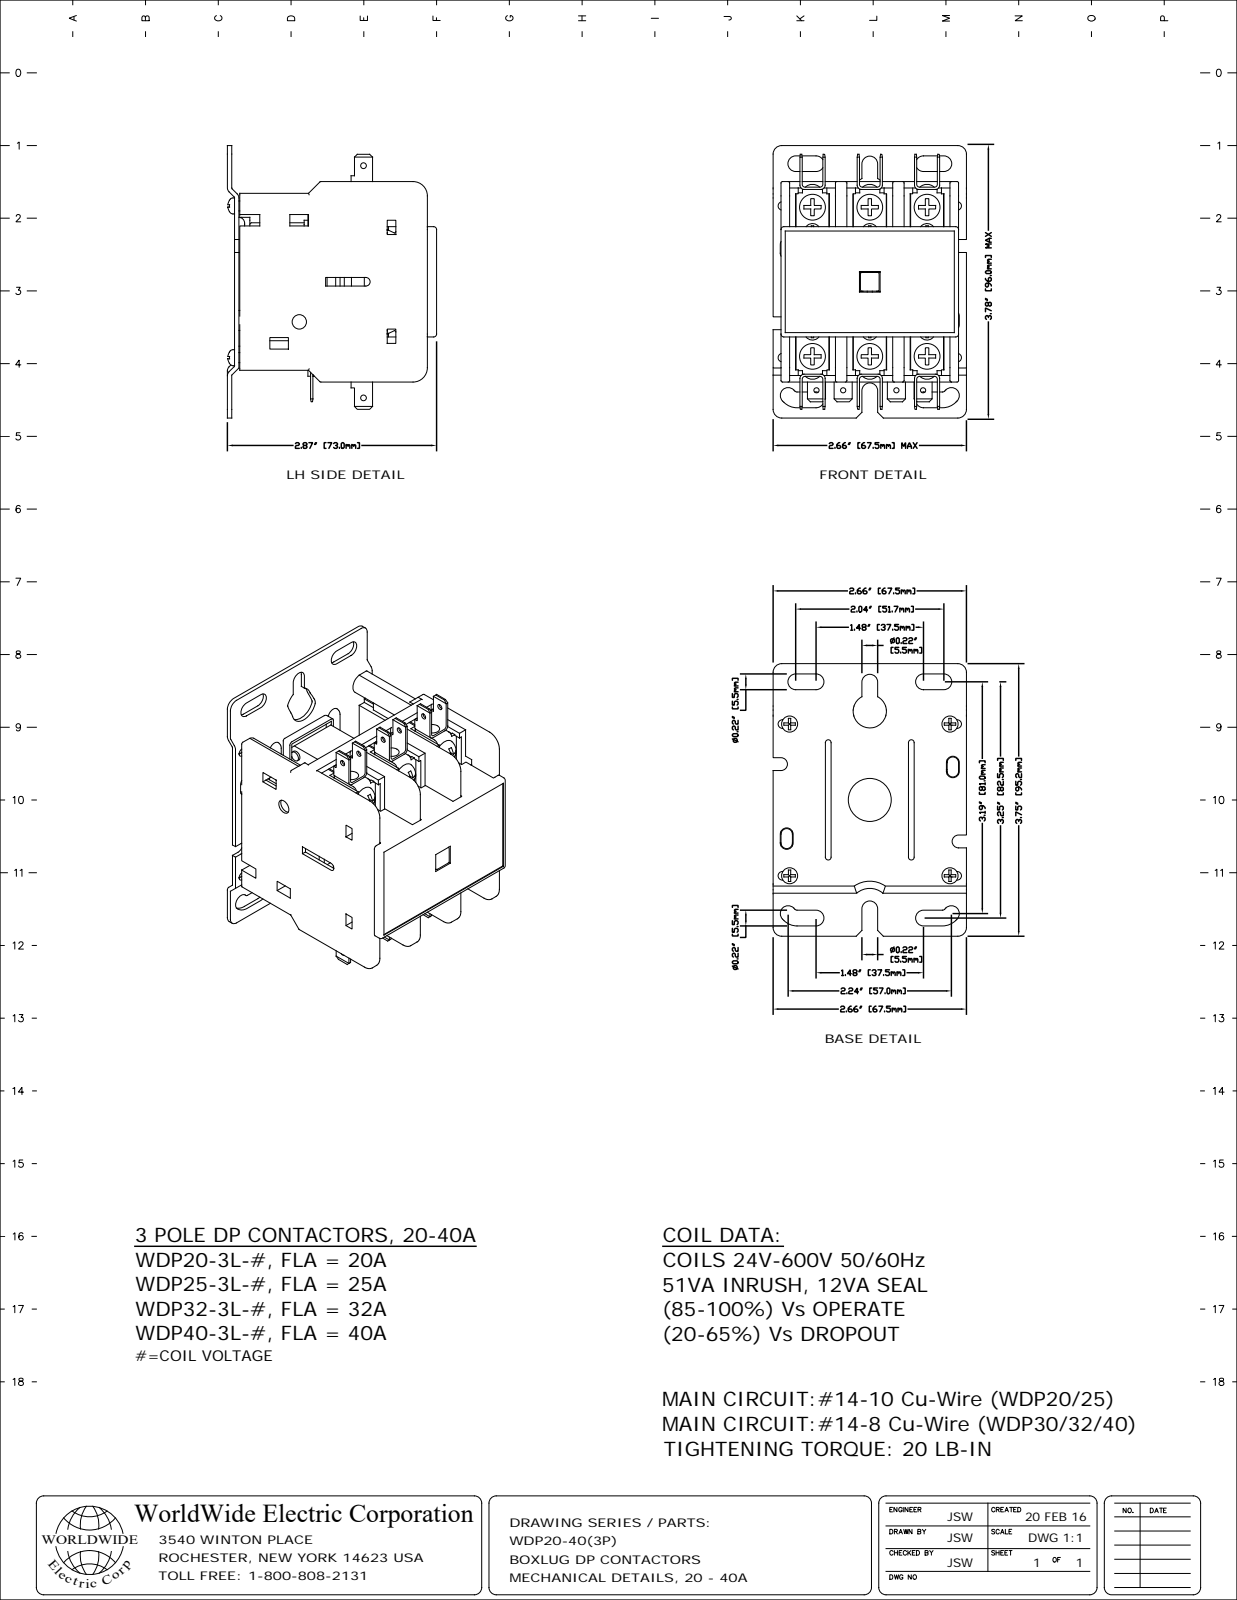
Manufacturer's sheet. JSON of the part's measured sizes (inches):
{"part_name": "WDP30-3L-120", "step_written_by": "SolidWorks 2017 (AUTOMOTIVE_DESIGN)", "units": "inches", "bodies": {"solids": 33, "faces": 3047, "planar": 1740, "cylindrical": 970, "other": 337}, "overall_size": [4.631, 3.079, 2.657], "volume_in3": 10.71, "surface_area_in2": 207.2, "round_holes": [[0.118, 6], [0.354, 6], [0.094, 4], [0.138, 4], [0.063, 2], [0.079, 2], [0.217, 2], [0.374, 2], [0.457, 1], [0.591, 1]], "round_bosses_or_shafts": [[0.138, 12], [0.374, 6], [0.551, 2], [0.276, 2], [0.177, 2]], "partial_cylinders_radius": [[0.02, 267], [0.008, 115], [0.039, 73], [0.059, 32], [0.079, 20], [0.118, 20], [0.108, 10], [0.004, 9]], "face_to_face_distances": [0.098, 0.827, 0.157, 2.598, 0.059, 0.197, 0.079, 2.441, 2.972, 0.748], "hole_center_spacings": [0.827, 0.929, 2.345, 0.423, 2.195, 0.388, 0.443, 0.846]}
